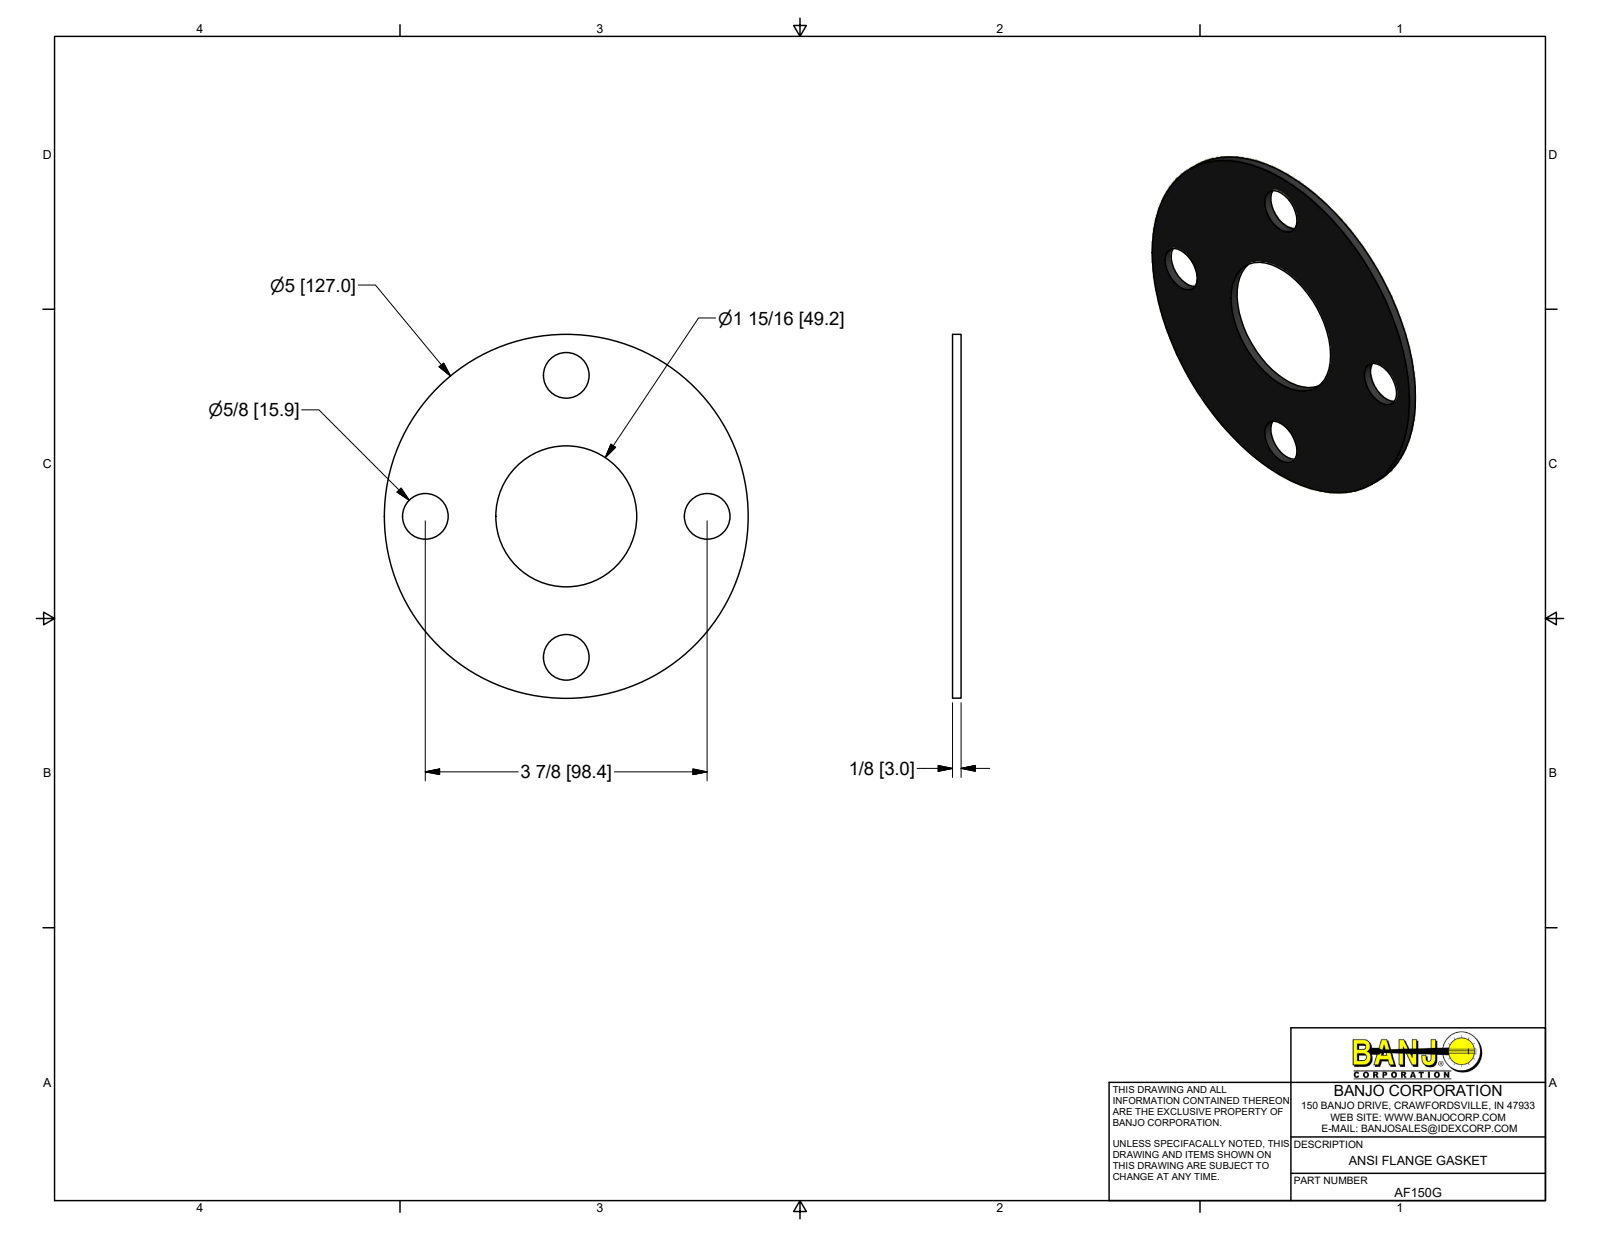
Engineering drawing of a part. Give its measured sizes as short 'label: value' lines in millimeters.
name: AF150G
written by: Autodesk Inventor 2017 (AUTOMOTIVE_DESIGN)
unit: mm
bodies: 1 solid, 8 faces (2 planar, 6 cylindrical, 0 other)
size: 127 × 127 × 3
volume: 29 894 mm³; area: 22 205 mm²
holes: 4× ⌀15.88, 1× ⌀49.21
bosses: 1× ⌀127
face distances: 3
hole spacings: 49.21, 69.59, 98.42
